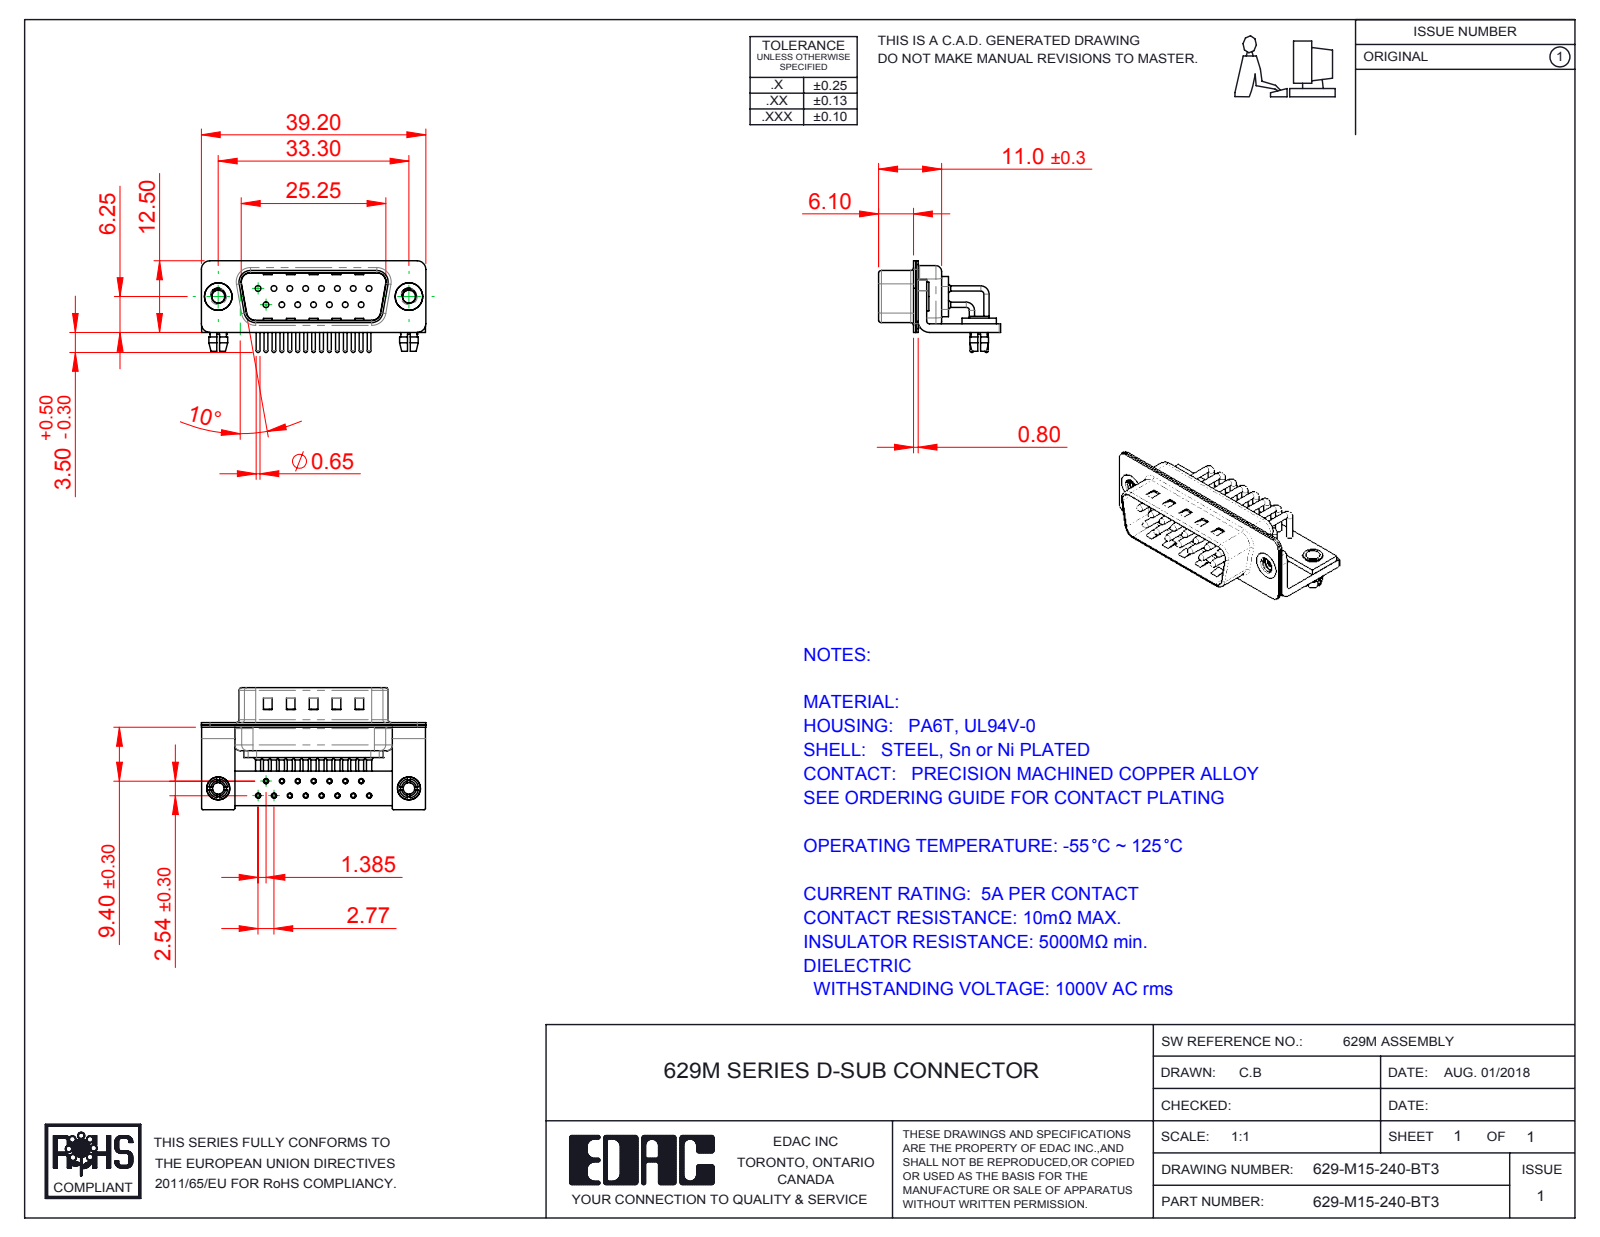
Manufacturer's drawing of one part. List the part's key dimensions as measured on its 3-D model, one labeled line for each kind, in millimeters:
Part name (STEP PRODUCT): 629M Board Lock; 629M Stabilizer Bracket; 629M 4-40 Threaded Rivet_Stabilizer; 629M Contact Row 1 (+6 more)
STEP written by: SolidWorks 2016 (CONFIG_CONTROL_DESIGN)
Units: millimetres
Bodies: 25 solids, 2162 faces (1173 planar, 757 cylindrical, 232 other)
Overall size (bounding box): 39.2 × 21.3 × 16
Volume: 2 481 mm³ · Surface area: 6 762 mm²
Round holes (diameter × count): ⌀2 ×17, ⌀0.9 ×15, ⌀1 ×15, ⌀1.7 ×15, ⌀2.26 ×2, ⌀2.5 ×2, ⌀3.2 ×2, ⌀4 ×2, ⌀4.8 ×2
Round bosses / shafts (diameter × count): ⌀0.9 ×21, ⌀1.5 ×15, ⌀0.65 ×15, ⌀5 ×2, ⌀4.9 ×2, ⌀4 ×2, ⌀3.4 ×2, ⌀3.3 ×2
Partial cylindrical surfaces — rounded edges, fillets, slot ends (radius × count): R0.25 ×16, R1.5 ×16, R1.01 ×15, R2 ×13, R0.5 ×9, R1.6 ×8, R0.6 ×4, R0.65 ×4
Main face-to-face distances: 0.4, 1.5, 0.85, 0.8, 1.25, 10.4, 9.55, 1, 1.9, 9.15
Hole centre spacings: 2.77, 5.54, 3.16, 8.31, 4.87, 11.08, 2.89, 7.37
